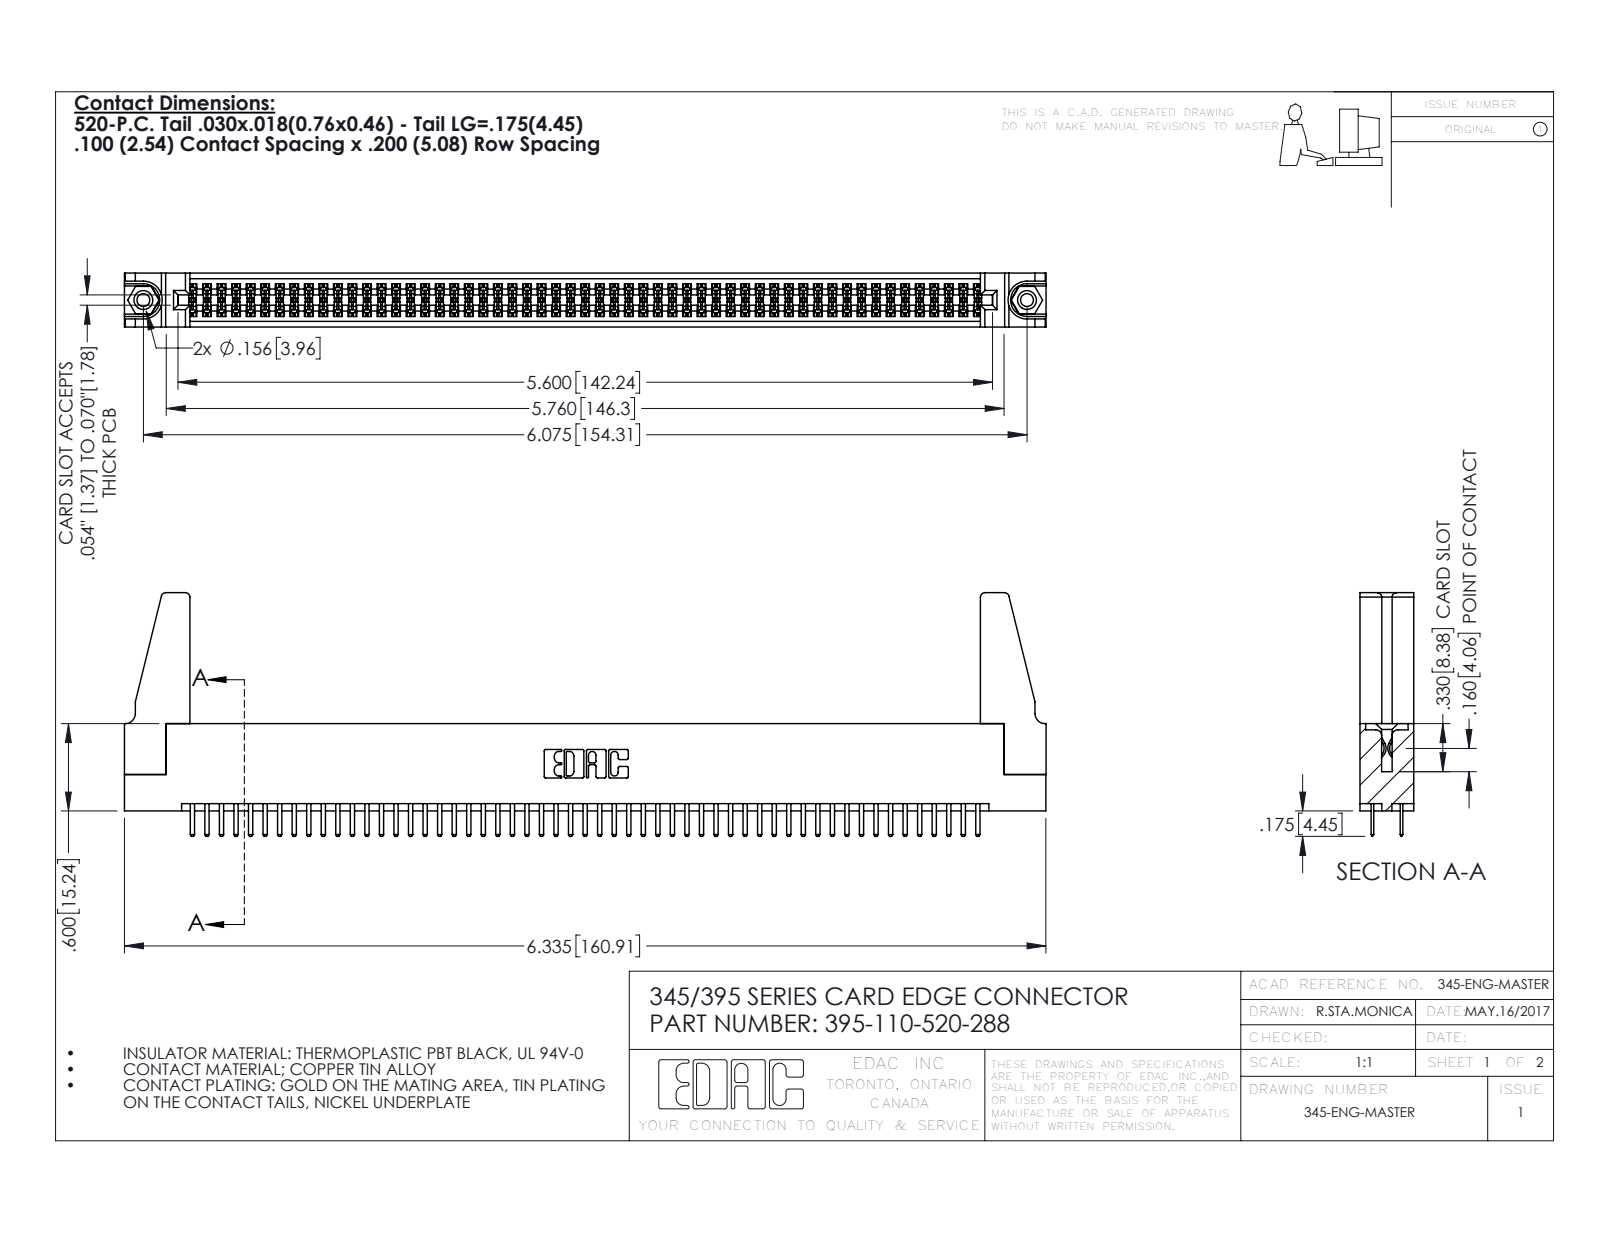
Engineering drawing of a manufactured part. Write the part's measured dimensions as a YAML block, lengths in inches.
part_name: "345-250-001_345-250-001-102; 345-292-001_345-293-120; 345 Part_Flush Mounting Lugs - 0.156 Dia-TH; 395-110-520-288 (+1 more)"
step_written_by: "SolidWorks 2016 (CONFIG_CONTROL_DESIGN)"
units: inches
bodies: {solids: 115, faces: 6190, planar: 4002, cylindrical: 2172, other: 16}
overall_size: [6.336, 1.675, 0.37]
volume: 1.157
surface_area: 41.05
round_holes:
  - {diameter: 0.089, count: 2}
  - {diameter: 0.125, count: 2}
  - {diameter: 0.156, count: 2}
  - {diameter: 0.064, count: 1}
round_bosses_or_shafts:
  - {diameter: 0.155, count: 2}
partial_cylinders:
  - {radius: 0.006, count: 165}
  - {radius: 0.01, count: 114}
  - {radius: 0.01, count: 22}
  - {radius: 0.03, count: 8}
  - {radius: 0.007, count: 6}
  - {radius: 0.031, count: 6}
  - {radius: 0.026, count: 3}
  - {radius: 0.014, count: 2}
face_to_face_distances: [0.072, 0.298, 0.37, 0.2, 0.098, 0.272, 0.025, 0.225, 0.022, 0.072]
hole_center_spacings: [0.27, 5.839, 6.075]
